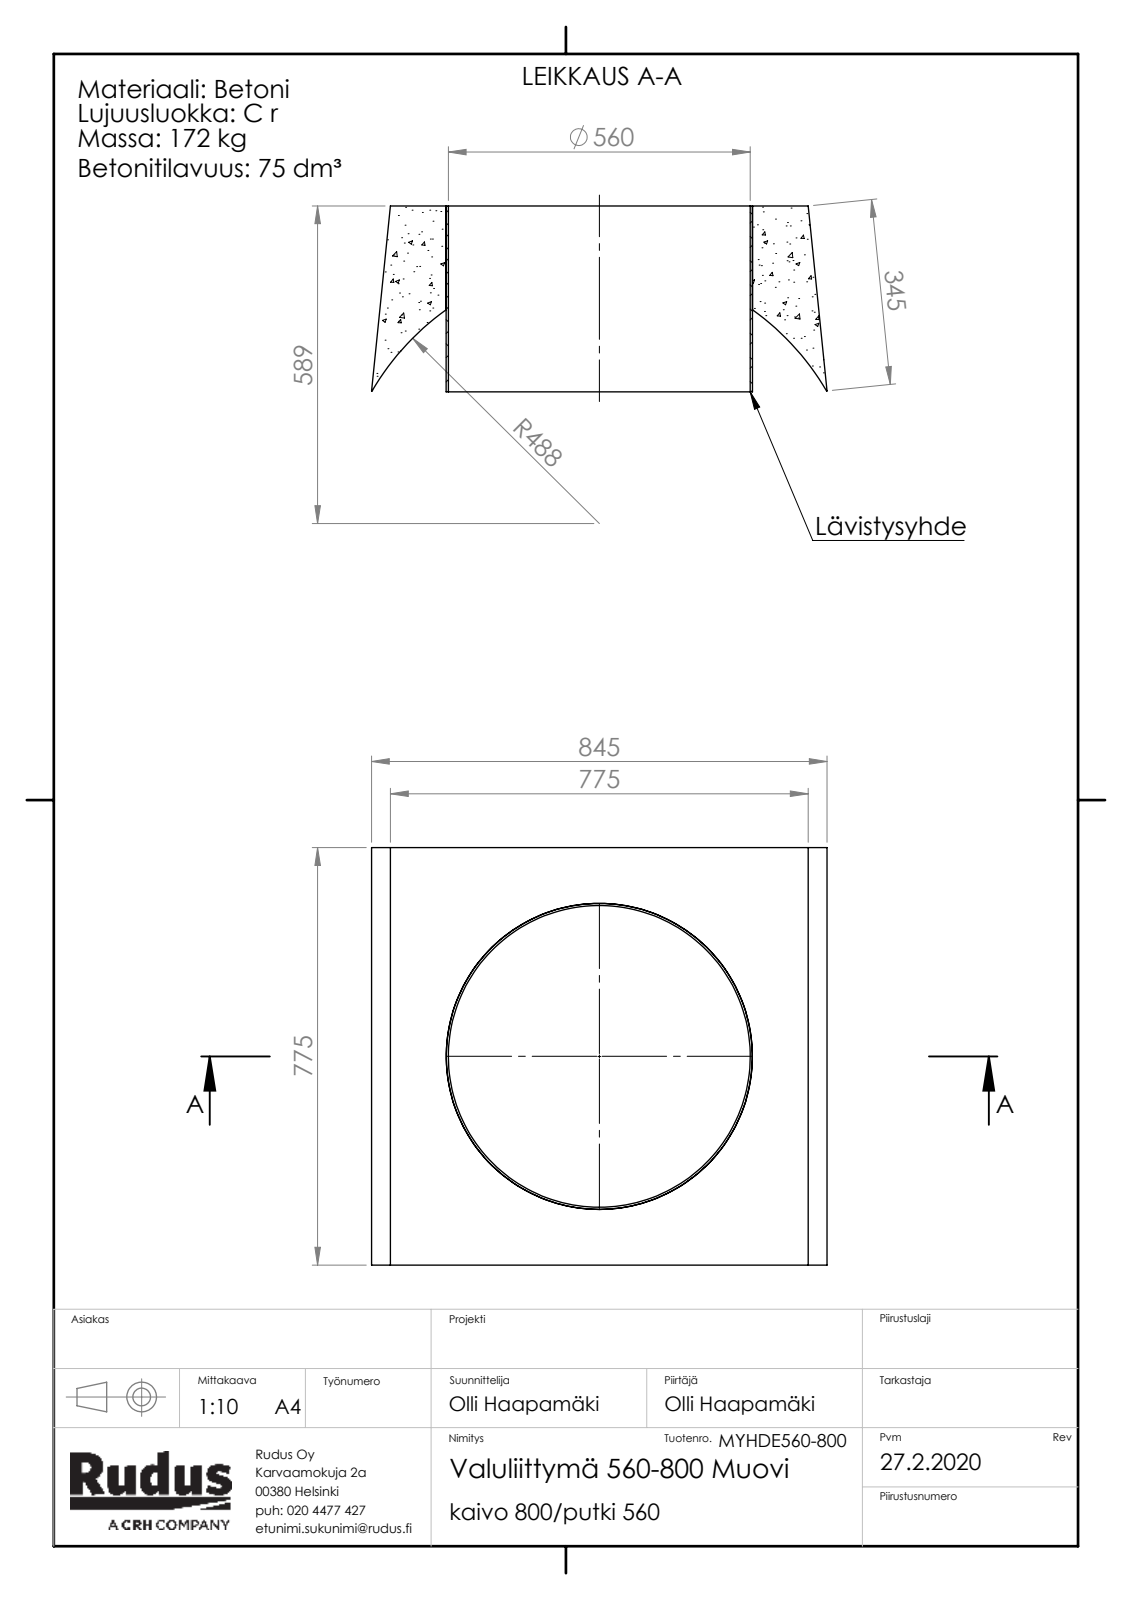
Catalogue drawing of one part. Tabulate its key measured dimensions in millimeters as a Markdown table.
| quantity | value |
| --- | --- |
| part name | kaivo-osa-valuliittyma-runko_muovi; Rudus MYHDE560-800 Valuliittymä 560-800 Muovi; muovi-lavistysyhde |
| STEP written by | SolidWorks 2019 (CONFIG_CONTROL_DESIGN) |
| units | millimeters |
| bodies | 2 solids, 16 faces (9 planar, 7 cylindrical, 0 other) |
| overall size | 845 × 775 × 345 |
| volume | 74 800 000 mm³ |
| surface area | 3 171 000 mm² |
| round holes (diameter × count) | 560 × 1, 568 × 1 |
| partial cylindrical surfaces (radius × count) | 488 × 1 |
| main face-to-face distances | 775, 345 |
